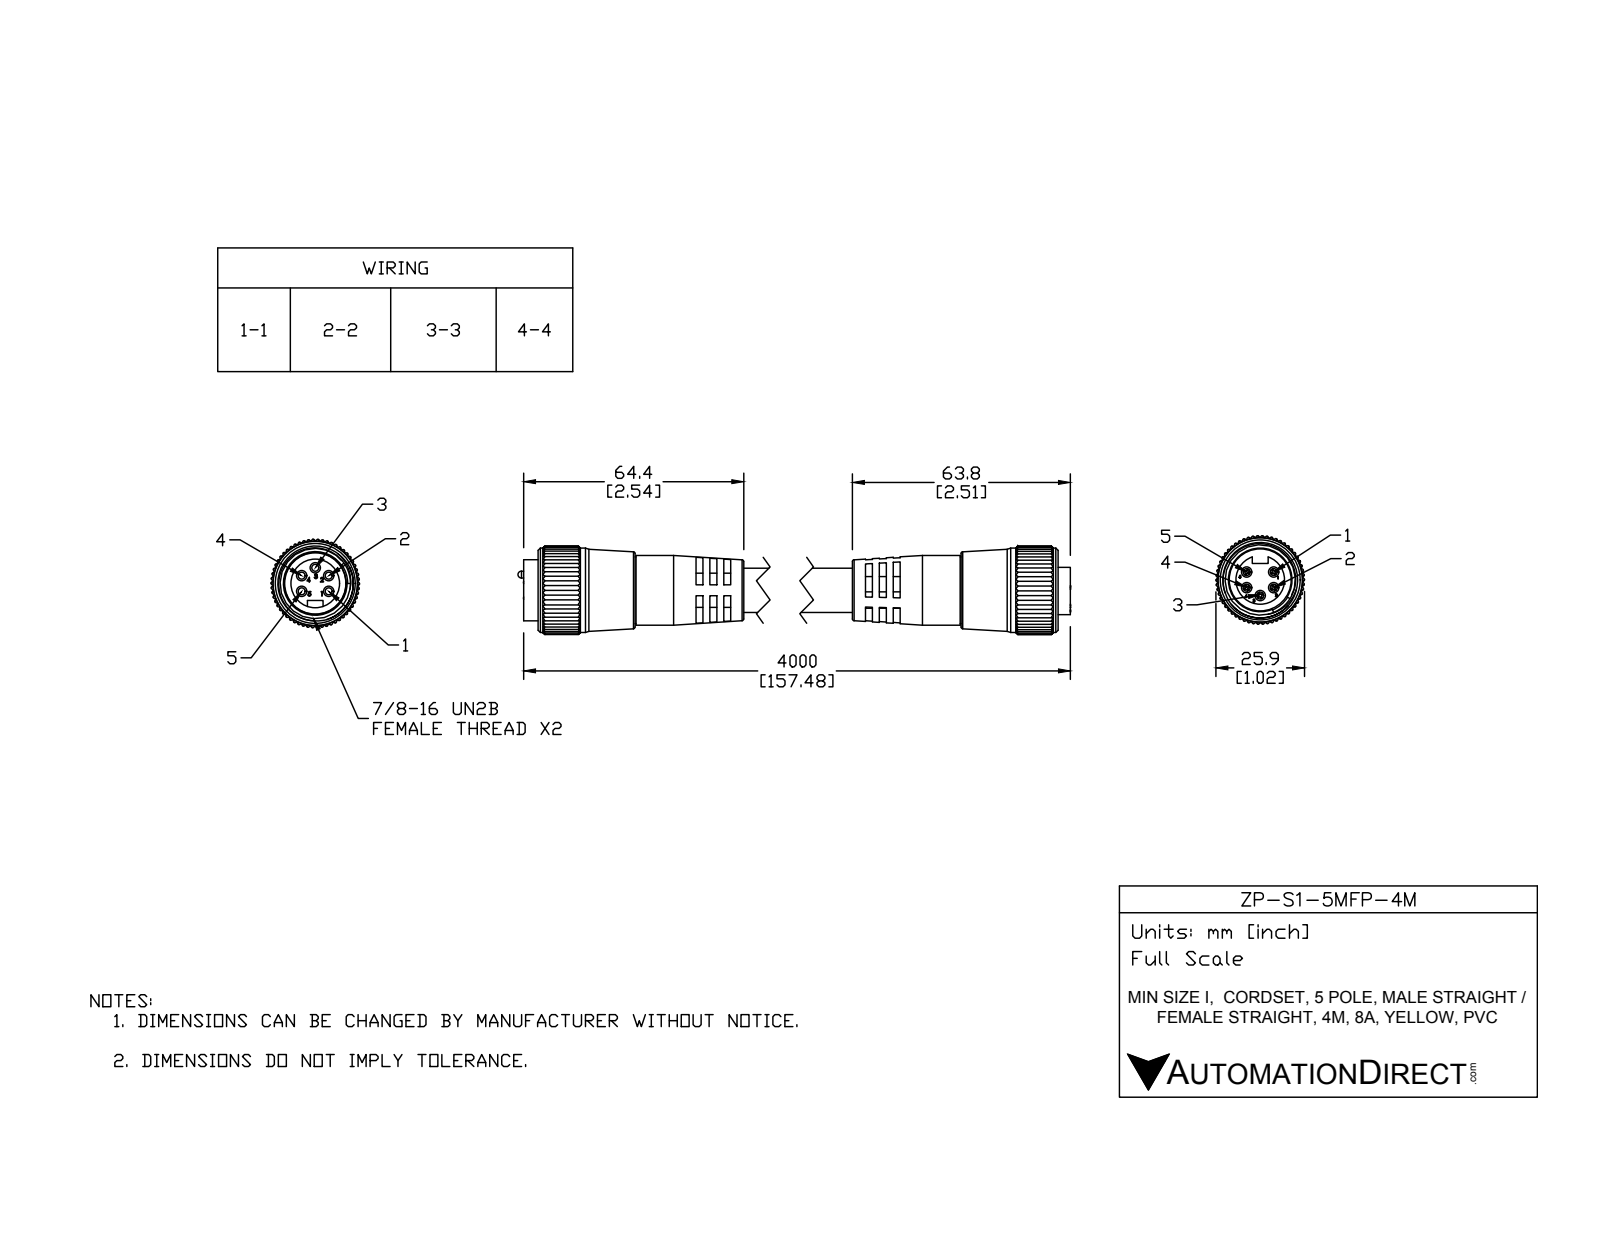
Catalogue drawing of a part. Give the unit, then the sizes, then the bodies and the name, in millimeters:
Units: millimetres
Overall size (bounding box): 229.66 × 25.84 × 25.83
Round holes (diameter × count): ⌀3.05 ×5, ⌀19.96 ×1, ⌀20.45 ×1, ⌀21 ×1
Round bosses / shafts (diameter × count): ⌀2 ×5, ⌀24.68 ×1, ⌀20.4 ×1, ⌀19.5 ×1, ⌀17.88 ×1, ⌀14.22 ×1, ⌀9.91 ×1, ⌀3.05 ×1
Partial cylindrical surfaces — rounded edges, fillets, slot ends (radius × count): R0.25 ×165, R2.29 ×1, R5.25 ×1, R12.93 ×1
Main face-to-face distances: 2, 4.02, 117.68, 113.65, 4.03, 125.74, 59.84, 4.04, 121.7, 121.72
Hole centre spacings: 4.57, 4.56, 7.91, 7.92, 9.14
Volume: 50 854 mm³ · Surface area: 23 442 mm²
Bodies: 9 solids, 1185 faces (439 planar, 630 cylindrical, 116 other)
Part name (STEP PRODUCT): ZP-S1-5MFP-4M
STEP written by: SolidWorks 2015 (AUTOMOTIVE_DESIGN)
